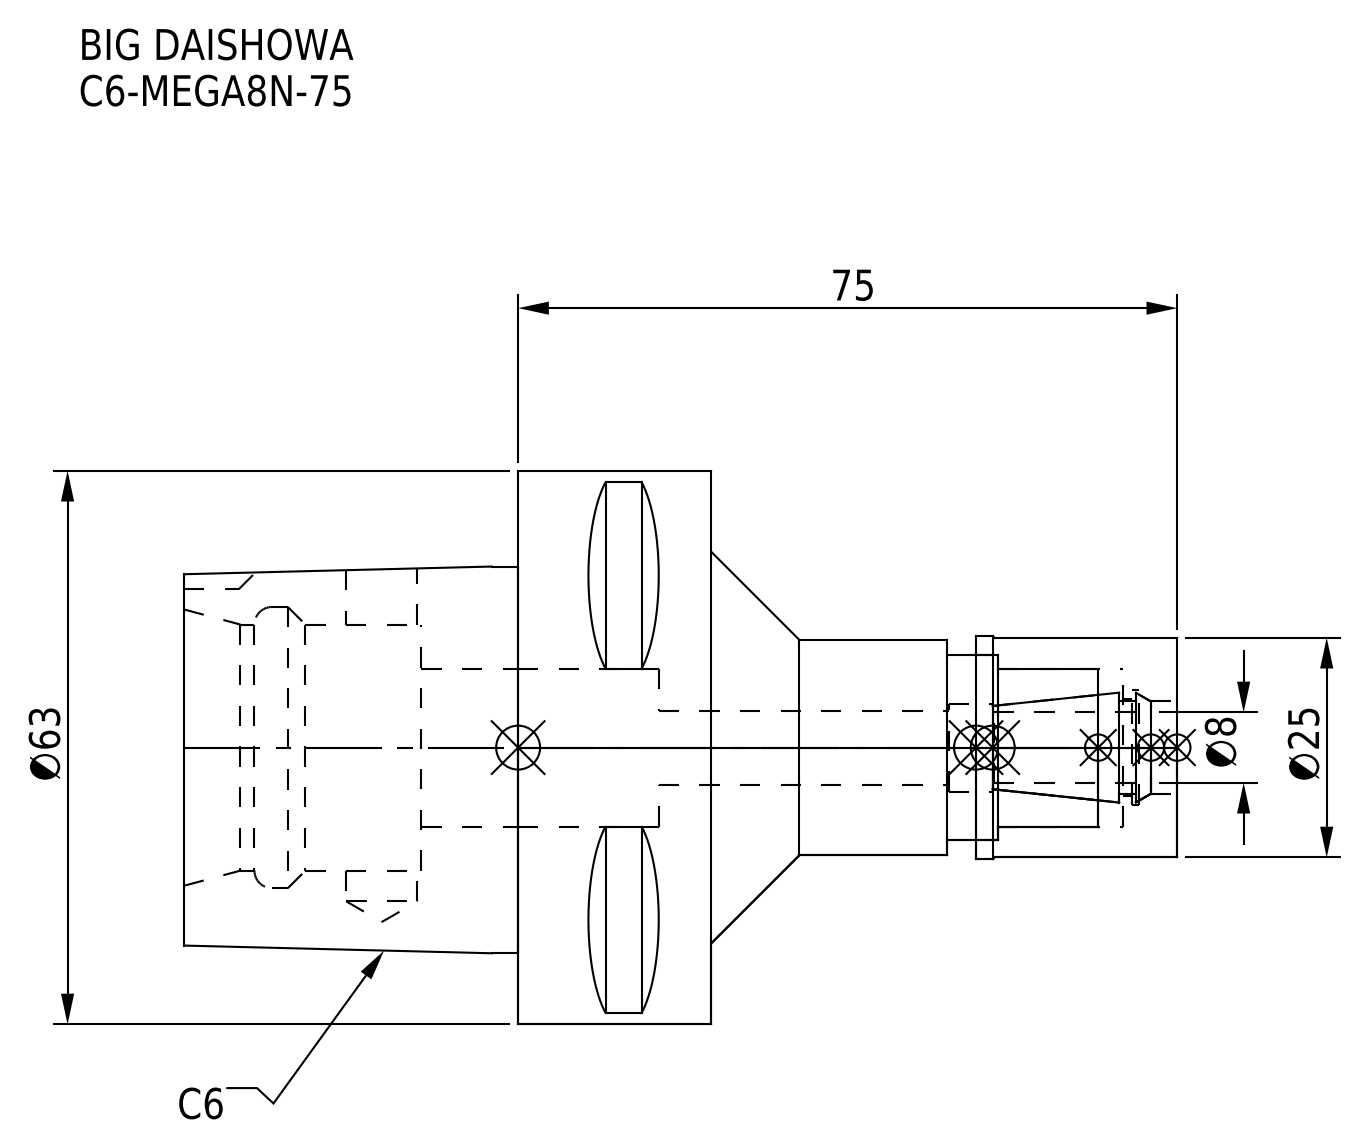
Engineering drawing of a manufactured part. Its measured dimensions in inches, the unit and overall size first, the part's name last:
Units: inches
Overall size (bounding box): 4.449 × 2.48 × 2.48
Round holes (diameter × count): ⌀0.319 ×1, ⌀0.331 ×1, ⌀0.394 ×1, ⌀0.413 ×1, ⌀0.433 ×1, ⌀0.512 ×1, ⌀0.709 ×1, ⌀0.827 ×1, ⌀1.102 ×1, ⌀1.26 ×1
Round bosses / shafts (diameter × count): ⌀2.48 ×1, ⌀0.996 ×1, ⌀0.984 ×1, ⌀0.965 ×1
Partial cylindrical surfaces — rounded edges, fillets, slot ends (radius × count): R0.197 ×1
Main face-to-face distances: 0.866, 1.063, 2.362, 1.496, 2.087, 2.953, 4.449, 1.299, 3.386, 0.433
Volume: 7.438 in³ · Surface area: 43.52 in²
Bodies: 2 solids, 95 faces (38 planar, 39 cylindrical, 18 other)
Part name (STEP PRODUCT): MGN8_1.stp; C6-MEGA8N-75-080-FreeParts; C6-MEGA8N-75_1.stp; C6-MEGA8N-75 (+3 more)
STEP written by: SolidWorks 2019 (CONFIG_CONTROL_DESIGN)
